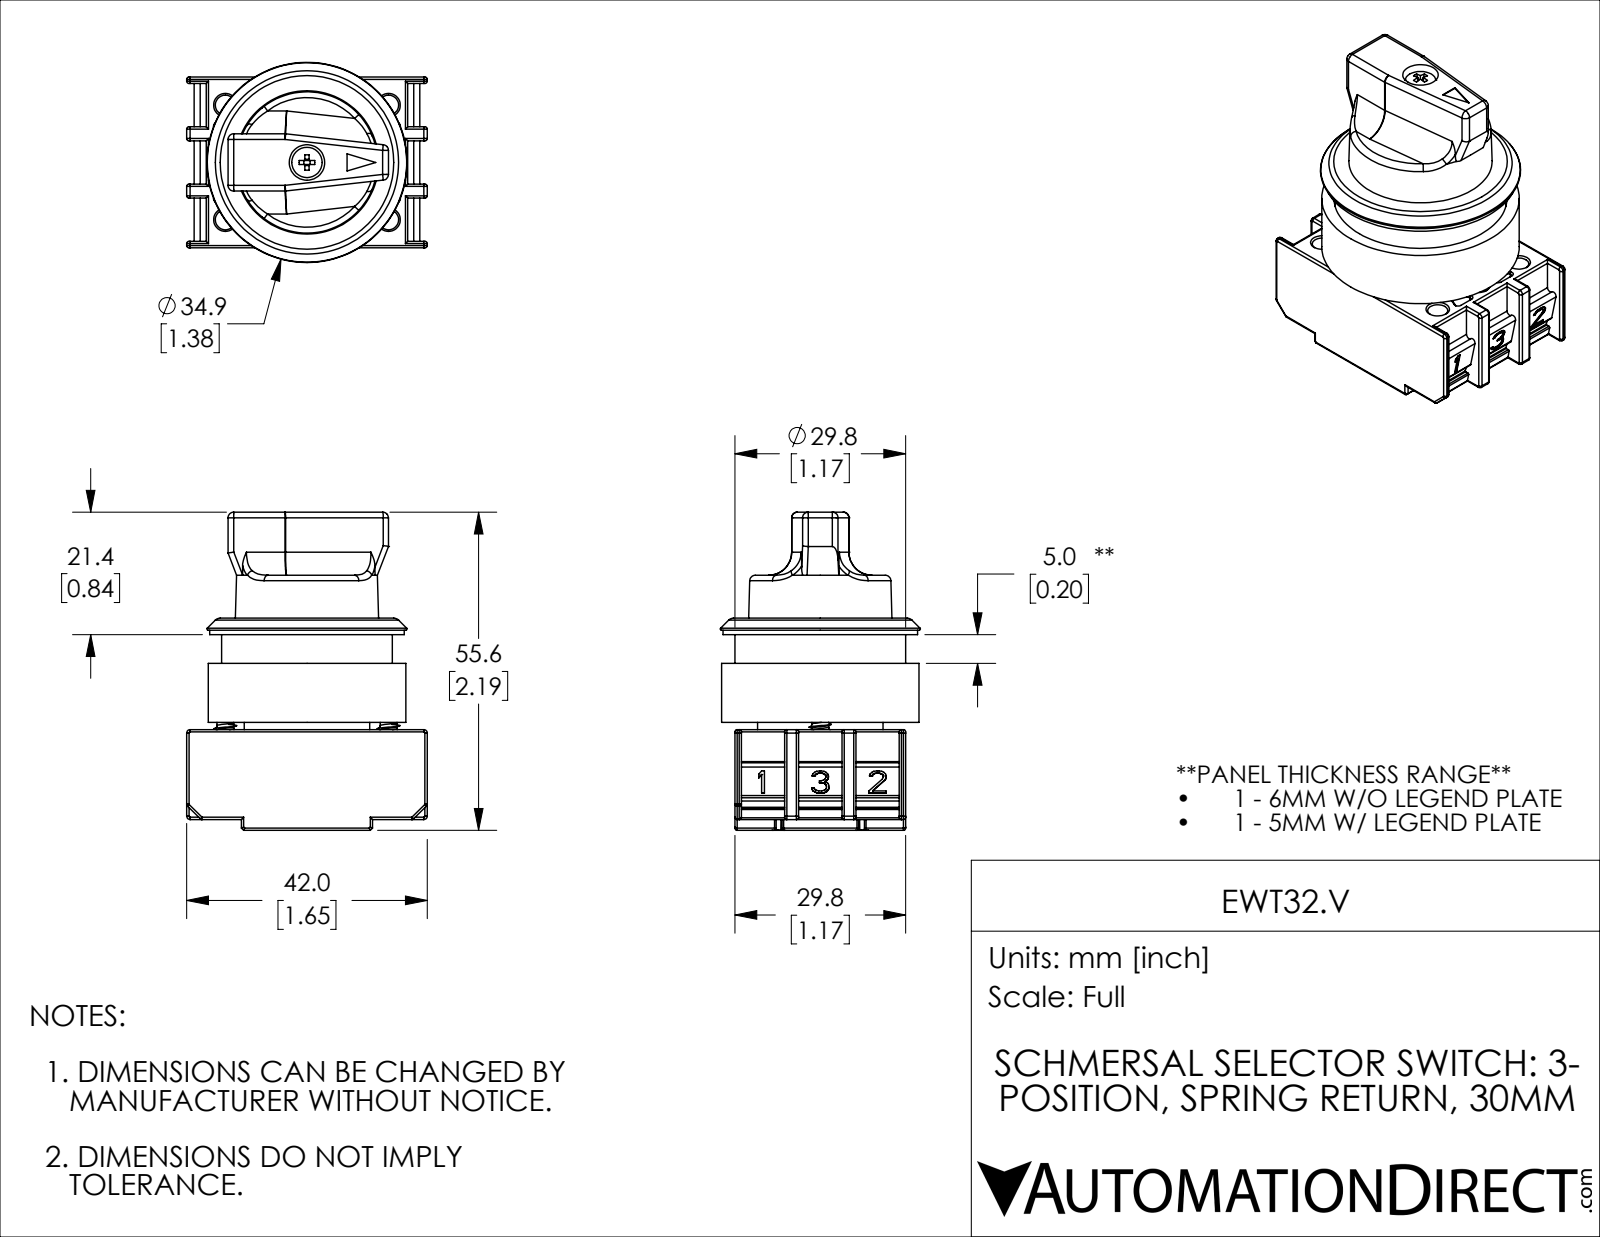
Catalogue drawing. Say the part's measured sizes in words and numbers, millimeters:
The part is named "EWT32.V". Its 3-D file was written by "SolidWorks 2019 (CONFIG_CONTROL_DESIGN)". It is 5 solids with 1701 faces: 641 planar, 592 cylindrical and 468 other. Overall it measures 55.55 by 42 by 34.93 millimeters. Its volume is 28 833 cubic millimeters and its surface area 25 882 square millimeters. Round holes: 6 of diameter 3.5, 6 of diameter 5.15, 4 of diameter 2, 4 of diameter 5, 2 of diameter 1.65, 2 of diameter 1.95, 1 of diameter 6.2, 1 of diameter 9.15, 1 of diameter 11, 1 of diameter 14, 1 of diameter 19, 1 of diameter 22. Round bosses or shafts: 4 of diameter 4.8, 2 of diameter 2.93, 1 of diameter 34.5, 1 of diameter 34, 1 of diameter 29.8, 1 of diameter 25.5, 1 of diameter 21.9, 1 of diameter 18.5. Partial cylindrical surfaces (rounded edges, fillets, slot ends): 120 of radius 0.4, 48 of radius 0.3, 30 of radius 1, 28 of radius 0.2, 14 of radius 0.5, 8 of radius 0.6, 6 of radius 0.8, 4 of radius 4. The main face-to-face distances are 16.1, 17.35, 18.85, 29.8, 18.2, 2.1, 18.3, 22.5, 37.05, 14.1. The hole center spacings are 14.33, 3.03, 4.24, 6, 6.26, 7.07, 9.01, 10.
